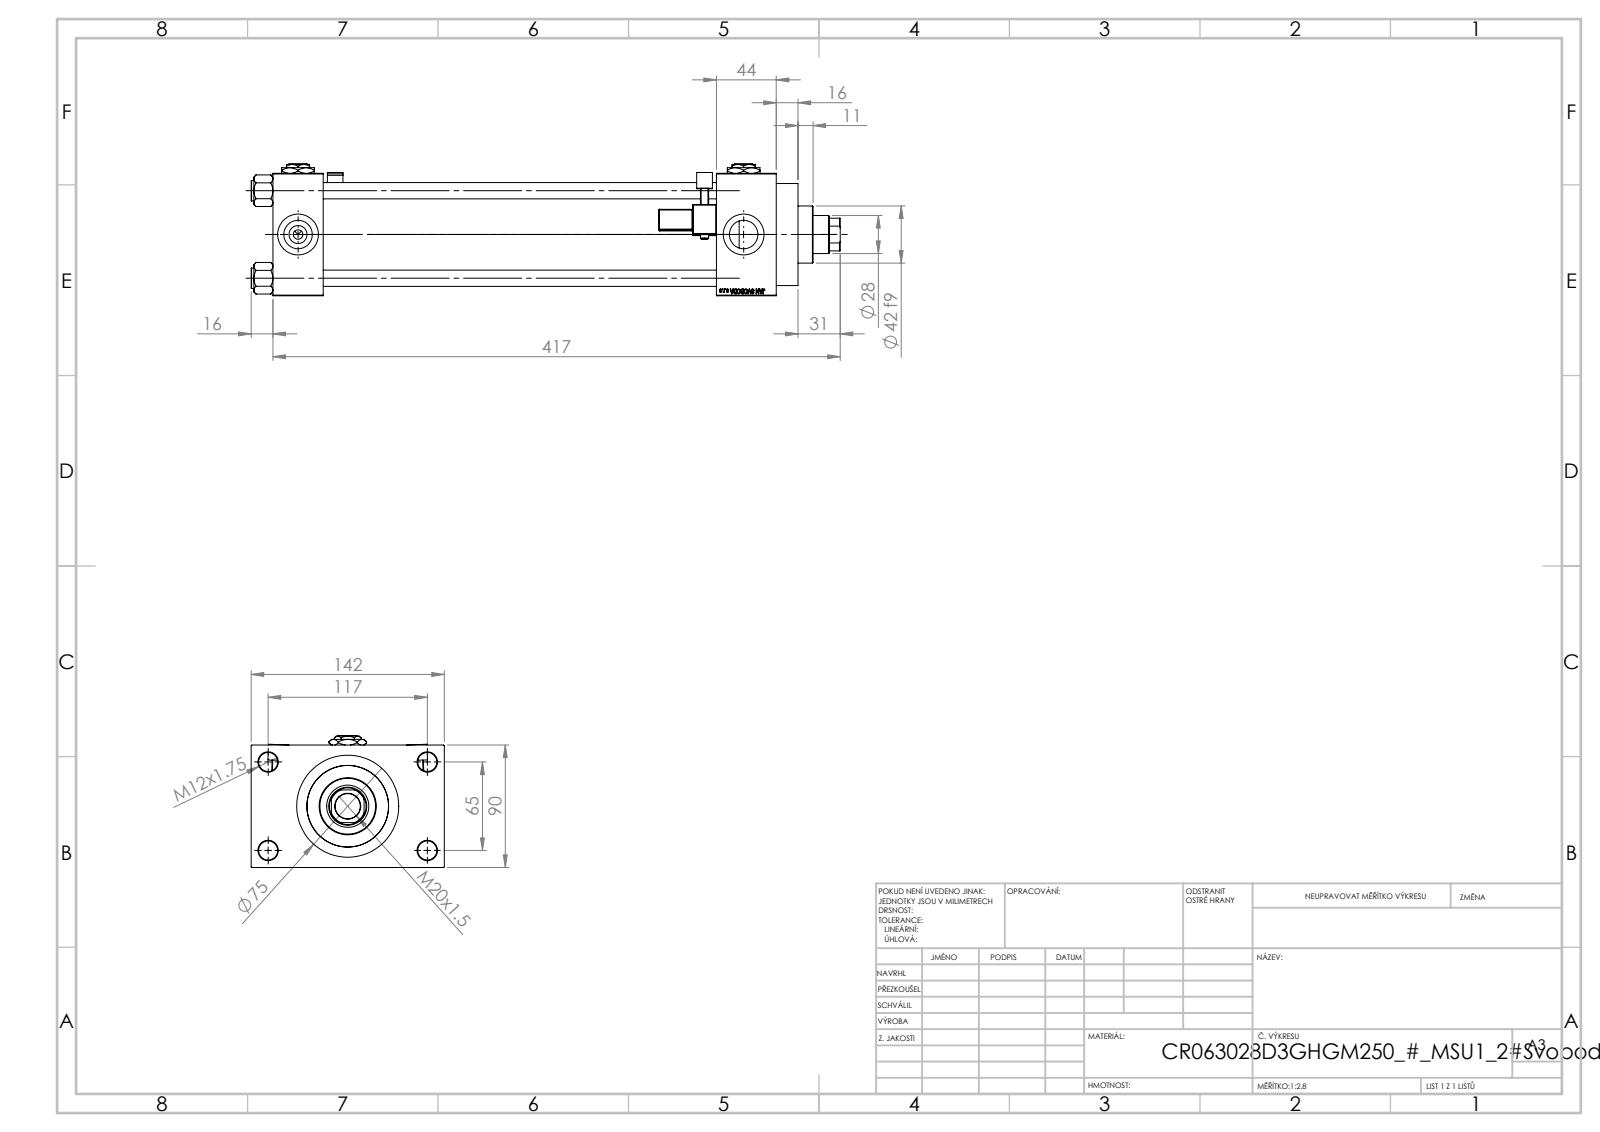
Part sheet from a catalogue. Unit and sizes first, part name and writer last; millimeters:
Units: millimetres
Overall size (bounding box): 433 × 142 × 97
Round holes (diameter × count): ⌀12 ×4, ⌀14 ×4, ⌀20.96 ×4, ⌀30 ×4, ⌀7 ×3, ⌀18.5 ×1, ⌀28 ×1, ⌀31 ×1, ⌀50 ×1, ⌀60 ×1, ⌀63 ×1
Round bosses / shafts (diameter × count): ⌀15 ×4, ⌀6 ×2, ⌀75 ×1, ⌀69 ×1, ⌀42 ×1
Partial cylindrical surfaces — rounded edges, fillets, slot ends (radius × count): R0.5 ×48, R1 ×2, R2.5 ×2, R4 ×2, R13.5 ×1
Main face-to-face distances: 90, 289, 37, 326, 370, 333, 44, 26, 116, 16
Hole centre spacings: 26.35, 45.47, 64.3, 66.92, 69.81, 90.65, 111.34, 65
Volume: 1 521 000 mm³ · Surface area: 367 504 mm²
Bodies: 15 solids, 1358 faces (603 planar, 159 cylindrical, 596 other)
Part name (STEP PRODUCT): NUT_M5_D; V215CR_D_TYCINKA; V215_VC_A; V215CR_MSU (+3 more)
STEP written by: SolidWorks 2019 (CONFIG_CONTROL_DESIGN)
